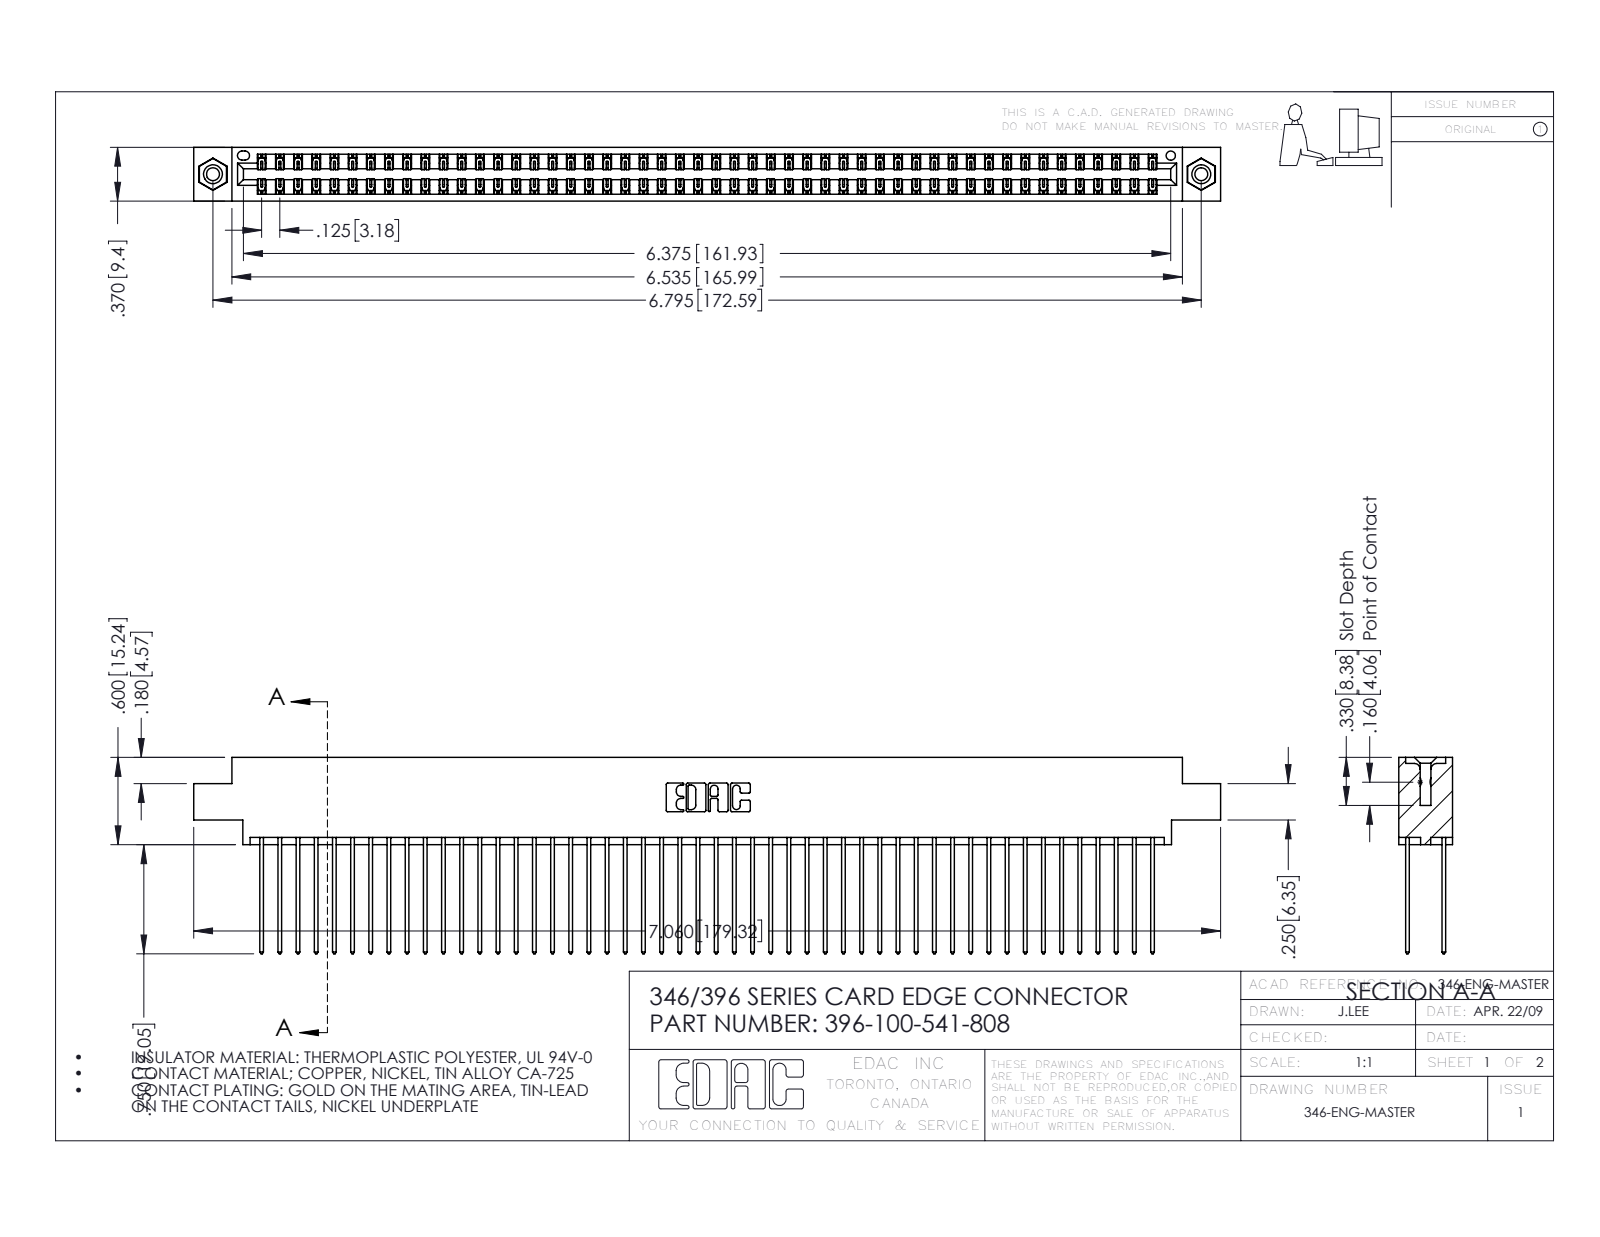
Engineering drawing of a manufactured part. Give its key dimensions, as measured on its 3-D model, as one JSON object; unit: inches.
{"part_name": "345-292-001_345-293-141; 396-100-541-808; 346 Part_0.170 Offset - 0.156 Dia-TI; 345-250-001_345-250-003-102", "step_written_by": "SolidWorks 2016 (CONFIG_CONTROL_DESIGN)", "units": "inches", "bodies": {"solids": 103, "faces": 5386, "planar": 3612, "cylindrical": 1758, "other": 16}, "overall_size": [7.06, 1.35, 0.37], "volume_in3": 1.096, "surface_area_in2": 43.04, "round_holes": [[0.089, 2], [0.125, 2], [0.156, 2], [0.064, 1]], "round_bosses_or_shafts": [[0.155, 2]], "partial_cylinders_radius": [[0.006, 150], [0.01, 100], [0.01, 22], [0.007, 6], [0.031, 6], [0.026, 3], [0.014, 2], [0.022, 2]], "face_to_face_distances": [0.048, 0.322, 0.25, 0.072, 0.298, 0.025, 0.37, 0.275, 0.225, 0.222], "hole_center_spacings": [0.246, 6.586, 6.795]}
